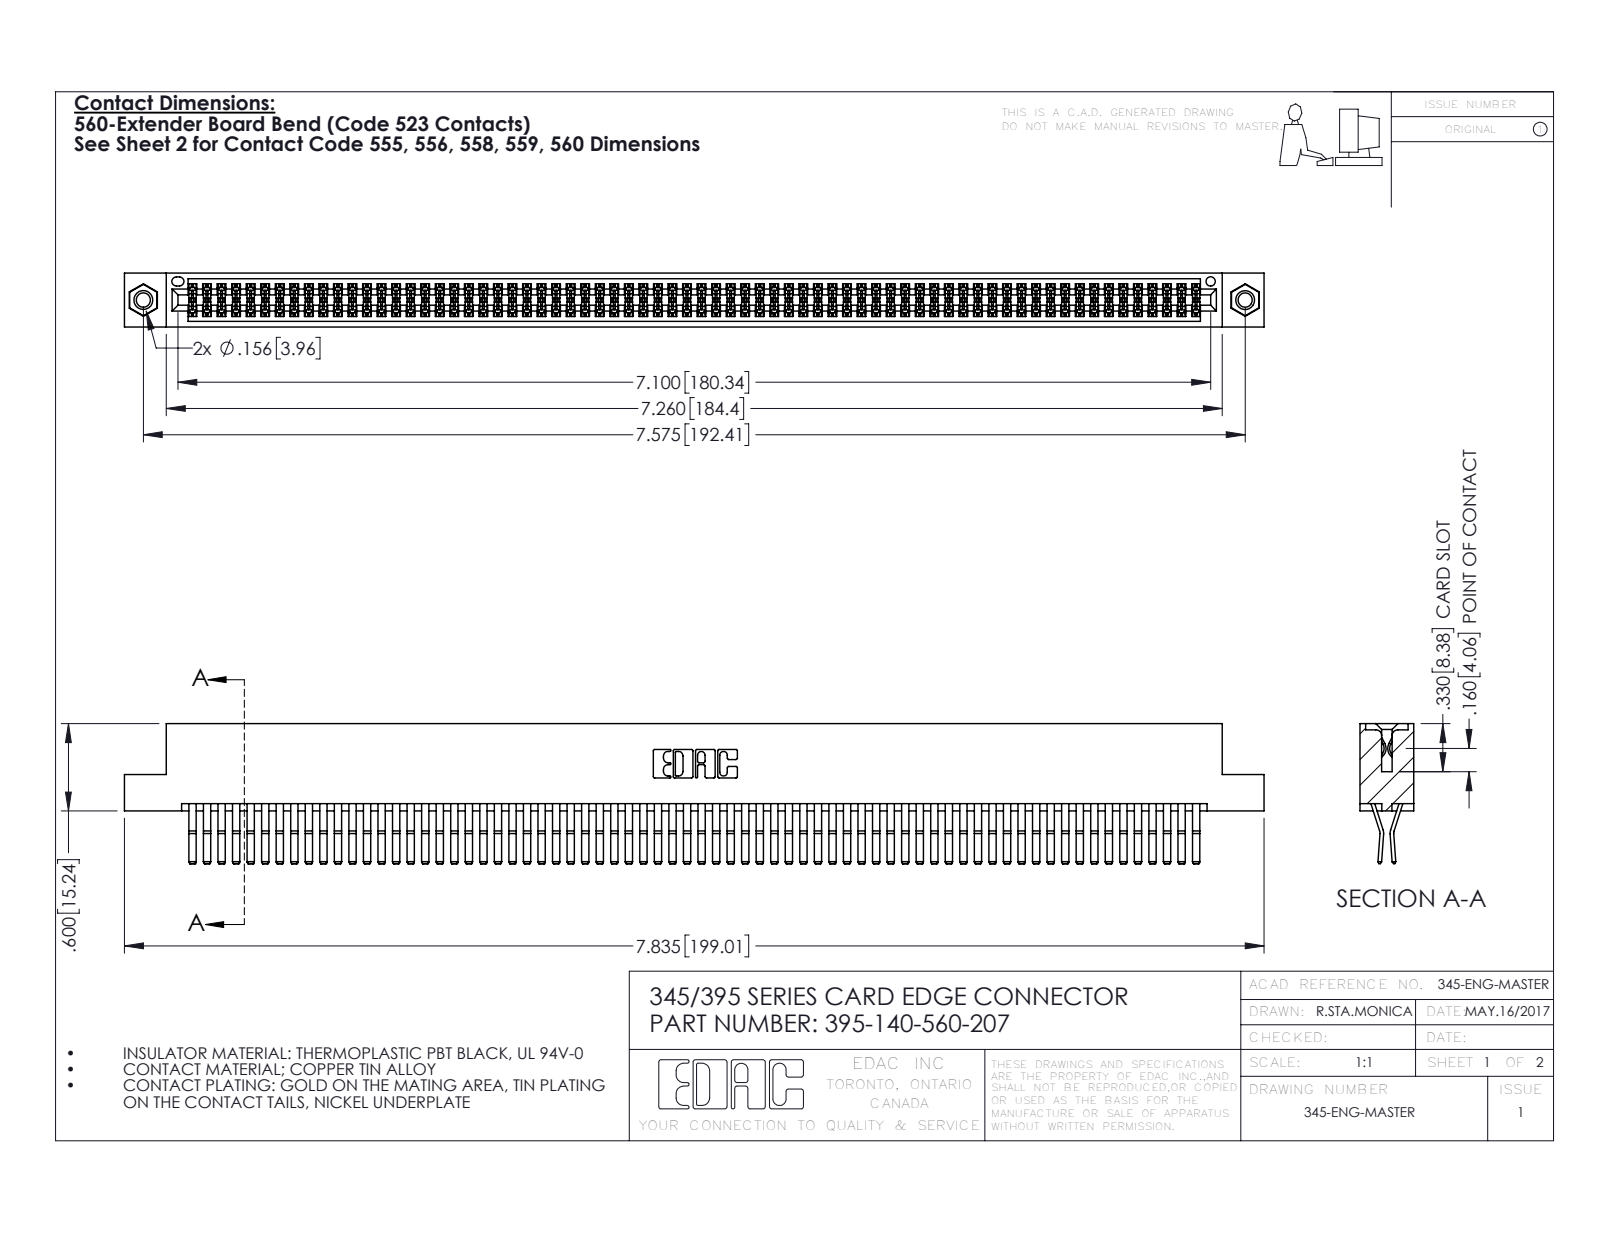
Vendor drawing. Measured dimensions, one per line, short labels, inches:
name: 345 Part_Flush Mounting Lugs - 0.156 Dia-TI; 345-250-001_345-250-005-103; 345-292-001_560 Tail; 395-140-560-207
written by: SolidWorks 2016 (CONFIG_CONTROL_DESIGN)
unit: in
bodies: 143 solids, 7466 faces (4732 planar, 2718 cylindrical, 16 other)
size: 7.835 × 0.962 × 0.37
volume: 1.251 in³; area: 51.5 in²
holes: 2× ⌀0.098, 2× ⌀0.125, 2× ⌀0.156, 1× ⌀0.064
bosses: 2× ⌀0.155
rounds: 210× R0.006, 22× R0.01, 6× R0.007, 6× R0.031, 3× R0.026, 2× R0.01, 2× R0.014, 2× R0.019
face distances: 0.025, 0.072, 0.298, 0.37, 0.2, 0.098, 0.272, 0.225, 0.175, 0.149
hole spacings: 0.27, 7.339, 7.575
